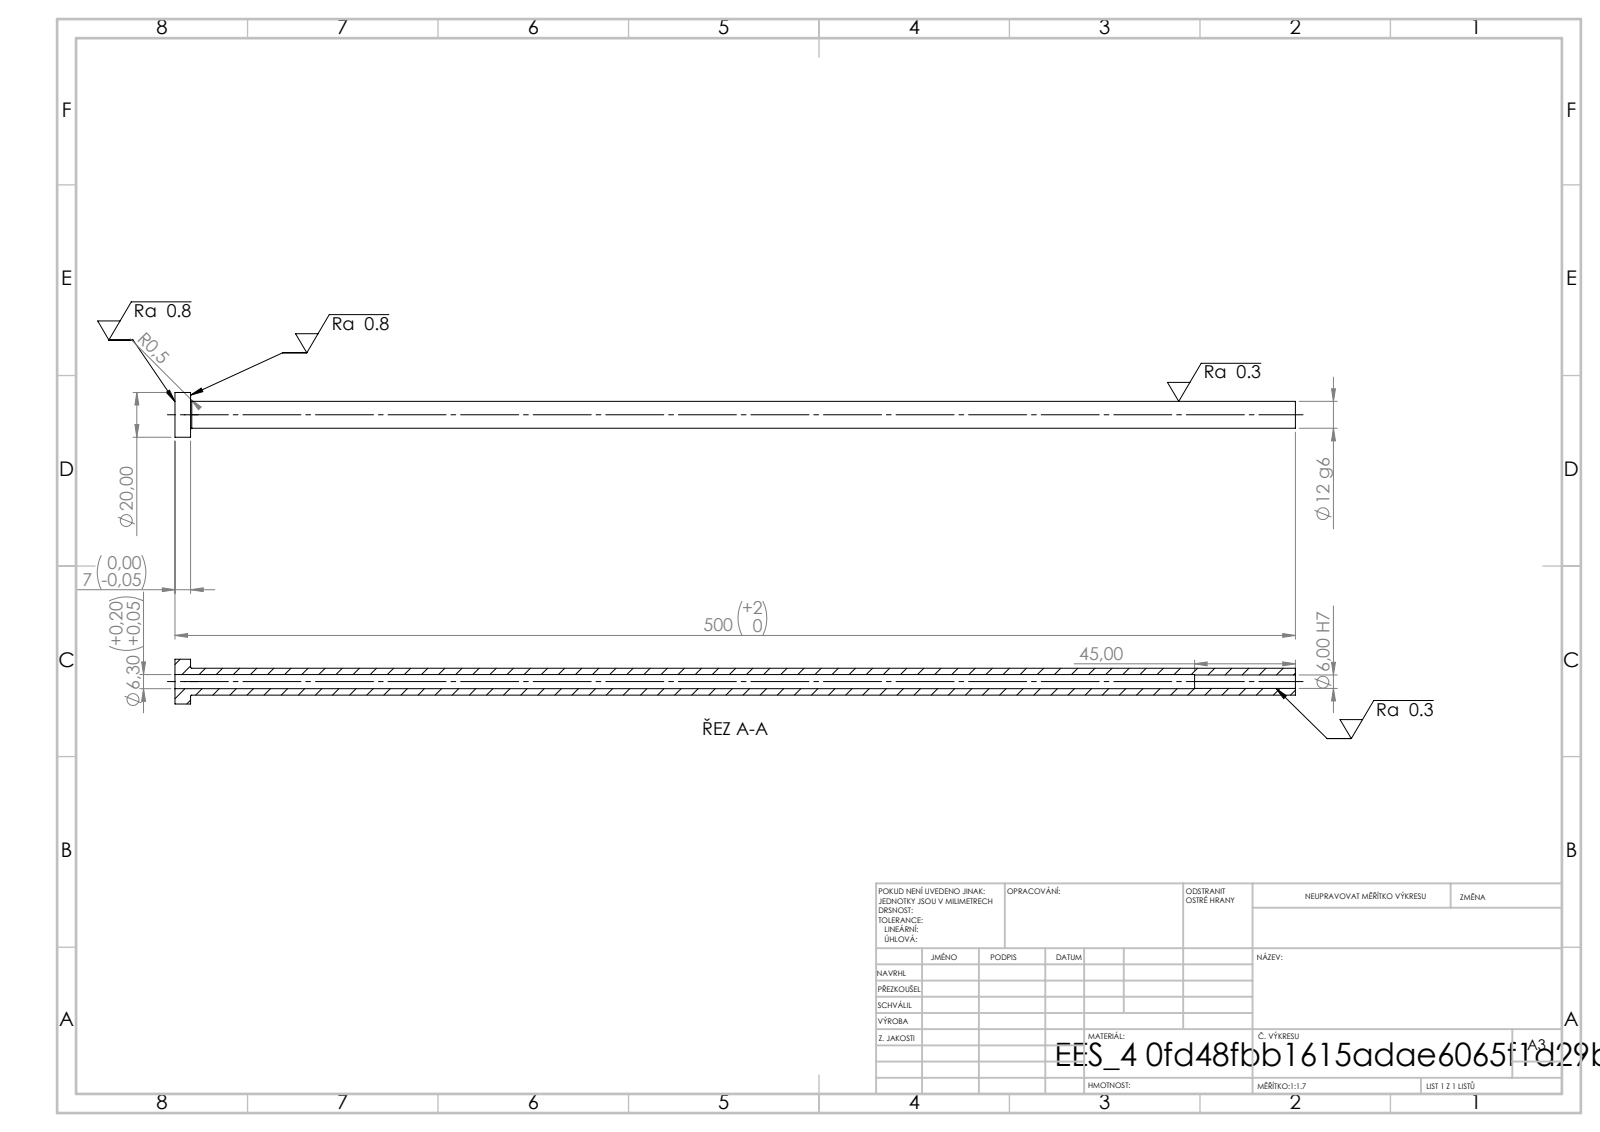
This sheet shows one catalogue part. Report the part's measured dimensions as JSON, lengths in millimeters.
{"step_written_by": "SolidWorks 2019 (CONFIG_CONTROL_DESIGN)", "units": "millimeters", "bodies": {"solids": 1, "faces": 14, "planar": 4, "cylindrical": 8, "other": 2}, "overall_size": [500, 20, 20], "volume_mm3": 42502, "surface_area_mm2": 29443, "round_holes": [[6, 1], [6.3, 1]], "round_bosses_or_shafts": [[20, 1], [12, 1]], "face_to_face_distances": [7, 500, 493, 455, 448, 45]}
